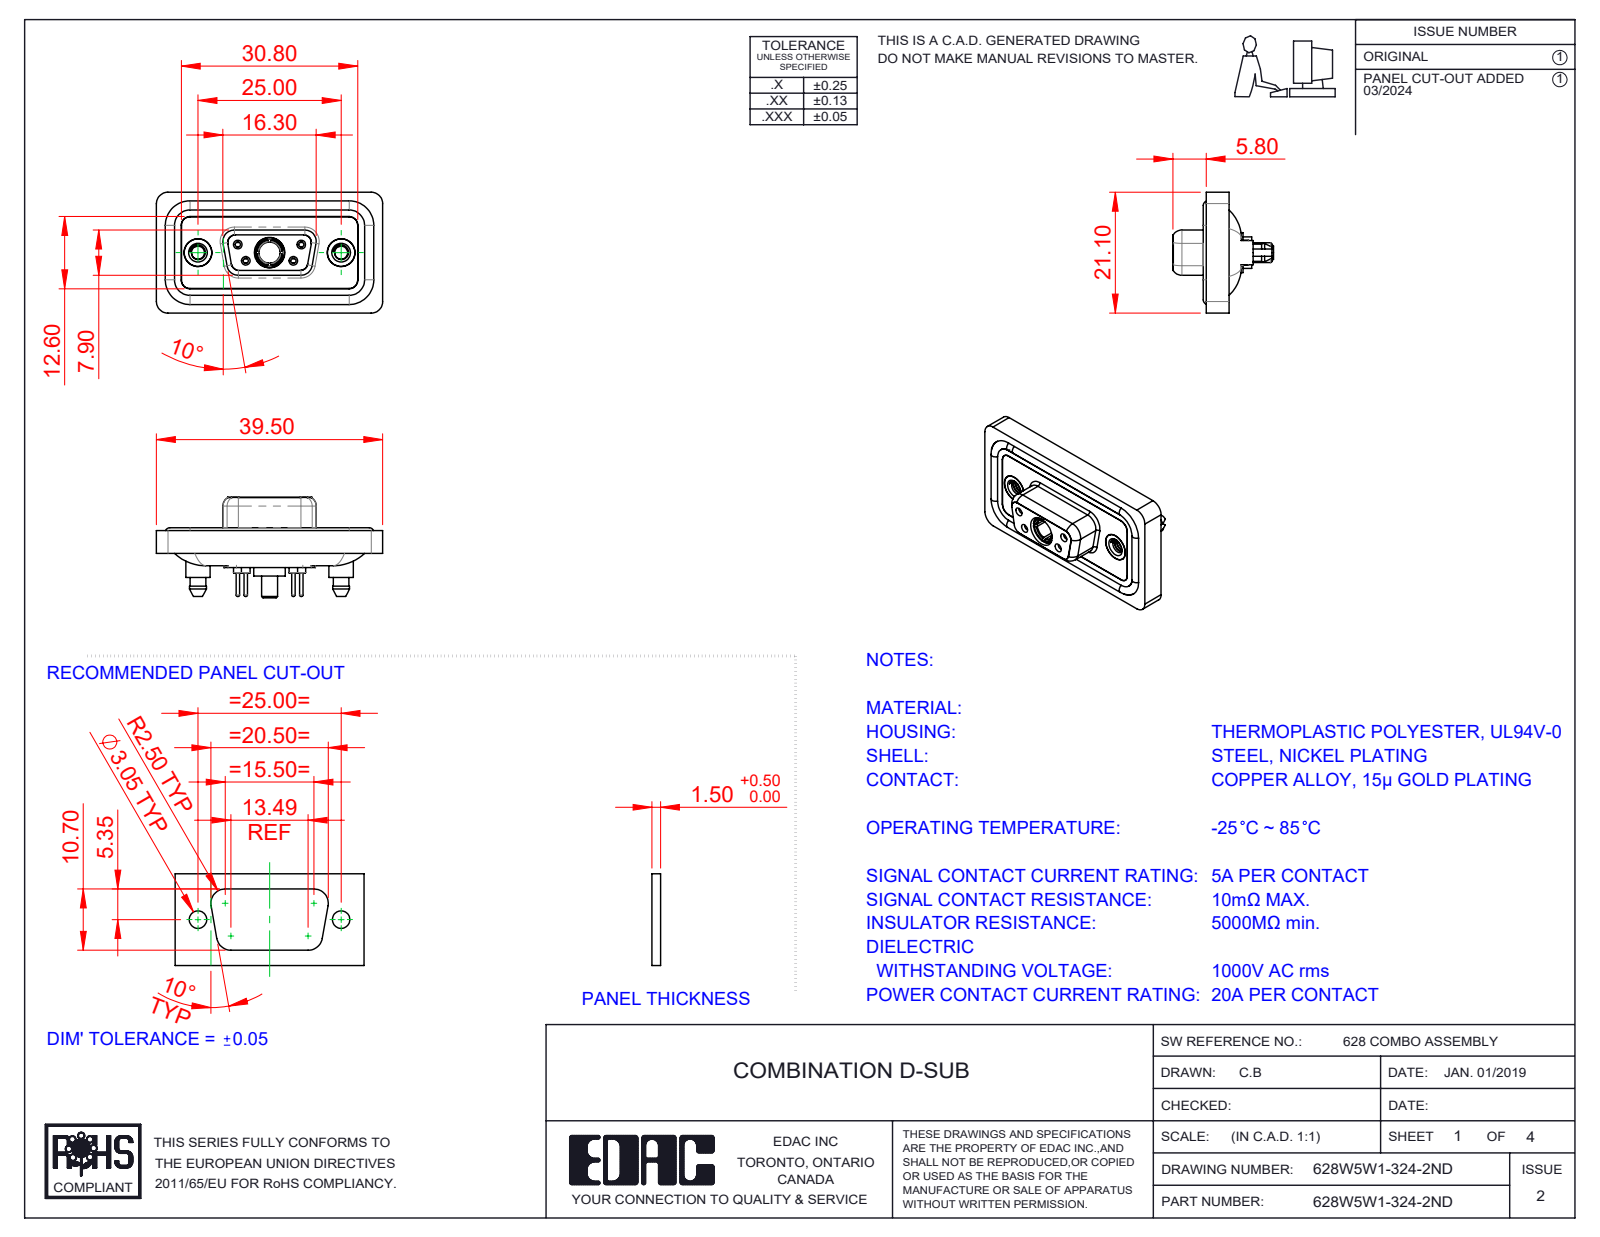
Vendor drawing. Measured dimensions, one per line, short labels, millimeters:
name: 628Combo Threaded Boardlock_D; 628Combo Waterproof Housing_09 Contacts; 628Combo Contact Row 2_24; 628Combo Shell Rear_09 Contacts (+5 more)
written by: SolidWorks 2023 (CONFIG_CONTROL_DESIGN)
unit: mm
bodies: 13 solids, 746 faces (210 planar, 335 cylindrical, 201 other)
size: 39.5 × 21.1 × 17.55
volume: 4 902 mm³; area: 7 975 mm²
holes: 4× ⌀0.9, 4× ⌀1.1, 4× ⌀1.5, 4× ⌀2, 3× ⌀4.85, 2× ⌀1.6, 2× ⌀1.7, 2× ⌀2.26, 2× ⌀4, 2× ⌀4.05, 2× ⌀5, 1× ⌀3.7
bosses: 6× ⌀1.6, 4× ⌀2.2, 4× ⌀0.6, 2× ⌀5.4, 2× ⌀4.95, 2× ⌀4.8, 2× ⌀4.25, 1× ⌀5.5
rounds: 24× R1.5, 18× R2, 10× R1.6, 8× R1.35, 4× R0.25, 4× R0.5, 4× R0.6, 4× R0.65
face distances: 0.4, 2.9, 1.1, 1.8, 1.6, 0.5, 5.65, 7.45, 5.35, 3.6
hole spacings: 3.16, 5.72, 7.1, 12.5, 18.1, 4.39, 4.4, 8.31
